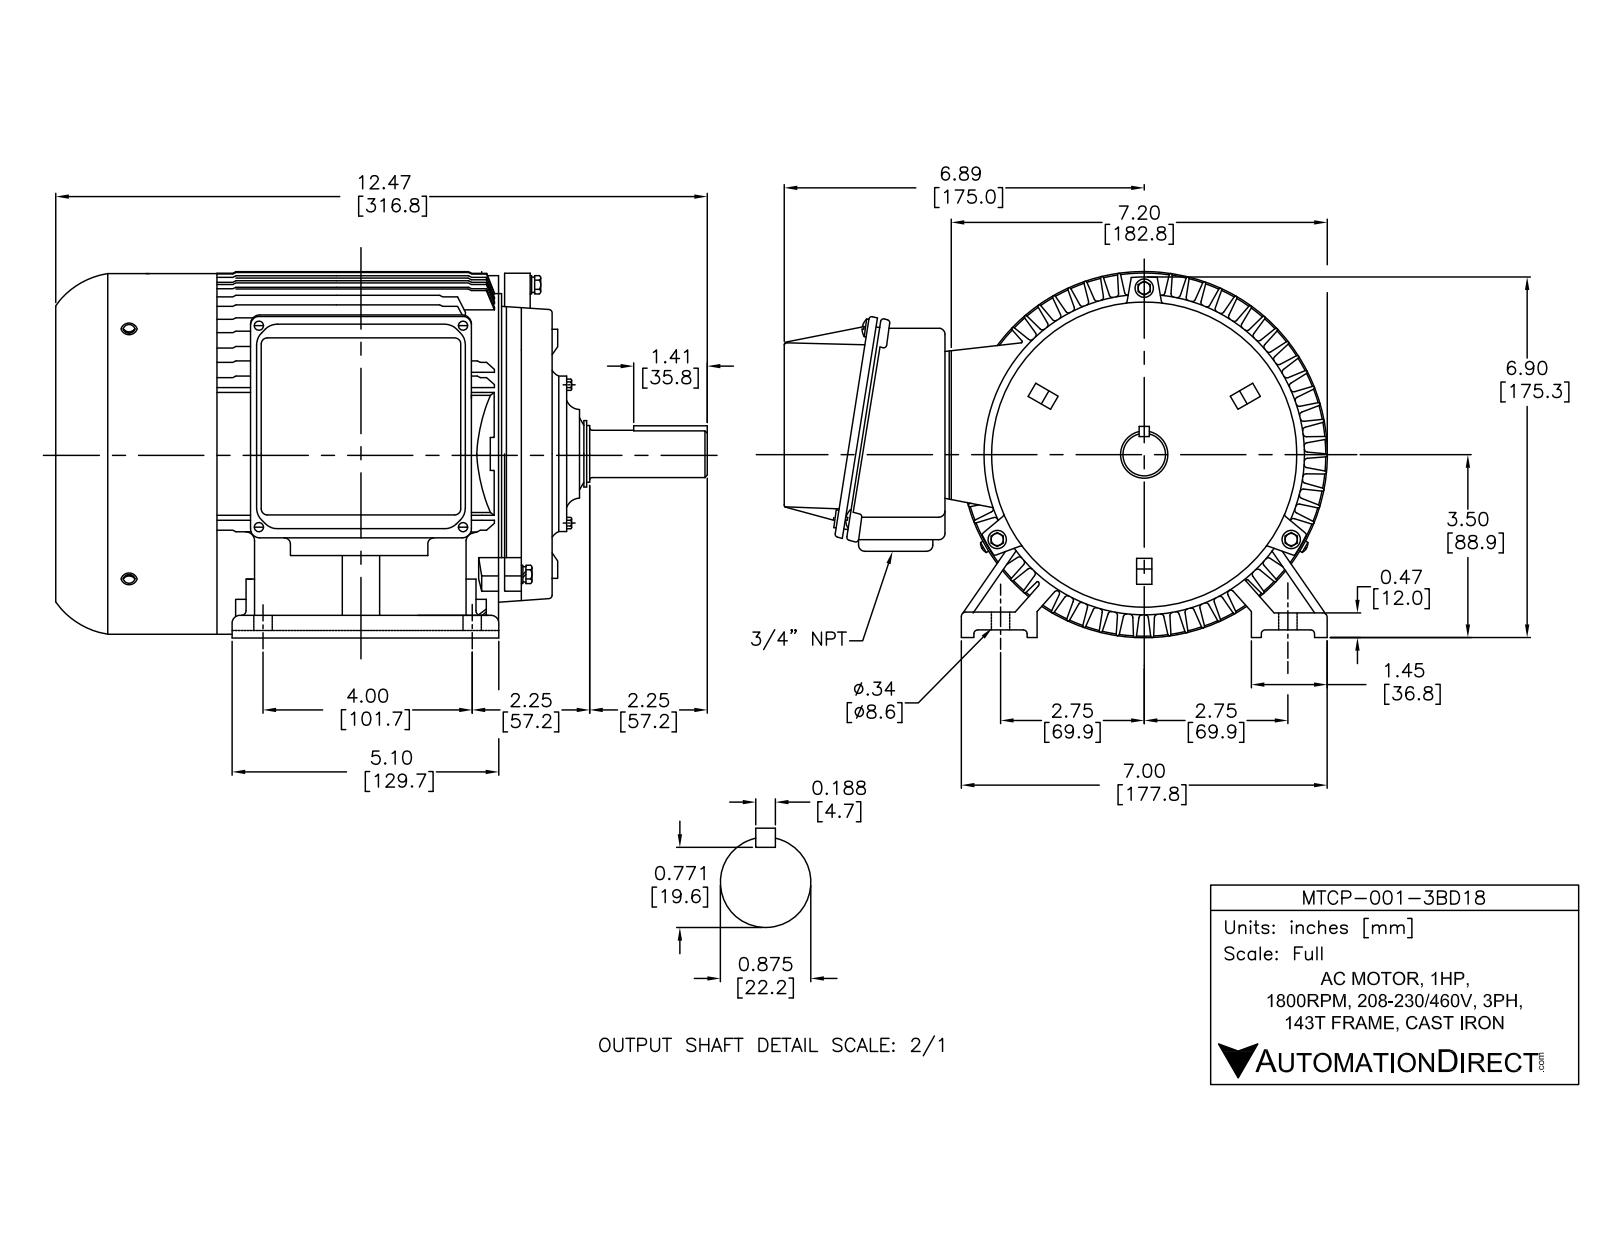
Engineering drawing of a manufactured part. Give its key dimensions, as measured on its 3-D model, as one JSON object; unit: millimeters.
{"part_name": "PE140接线盒座_默认_按加工; PE140标准前端盖; spring lock washers--normal type gb_GB_FASTENER_WASHER_SW 6; hex head bolts-full thread grade c gb_GB_FASTENER_BOLT_HHBFTC M6X35-N (+6 more)", "step_written_by": "SolidWorks 2017 (AUTOMOTIVE_DESIGN)", "units": "millimeters", "bodies": {"solids": 47, "faces": 2450, "planar": 722, "cylindrical": 964, "other": 764}, "overall_size": [347.55, 246.78, 182.39], "volume_mm3": 1685000, "surface_area_mm2": 685884, "round_holes": [[5.8, 14], [4.2, 11], [9, 8], [2, 4], [5, 3], [5.3, 3], [5.4, 3], [6.4, 3], [6.68, 3], [7, 3], [7.69, 3], [8, 1]], "round_bosses_or_shafts": [[5, 11], [12, 3], [10, 3], [9.88, 3], [8, 3], [6, 3], [175.4, 1], [173, 1]], "partial_cylinders_radius": [[0.5, 145], [1, 85], [2, 60], [1.25, 27], [7, 21], [1.2, 20], [0.34, 16], [3, 15]], "face_to_face_distances": [4, 6, 2, 3, 1.2, 12, 214, 217, 65.05, 63.85], "hole_center_spacings": [54, 90, 25.4, 76.37, 101.6, 139.7, 141.99, 172.74]}
